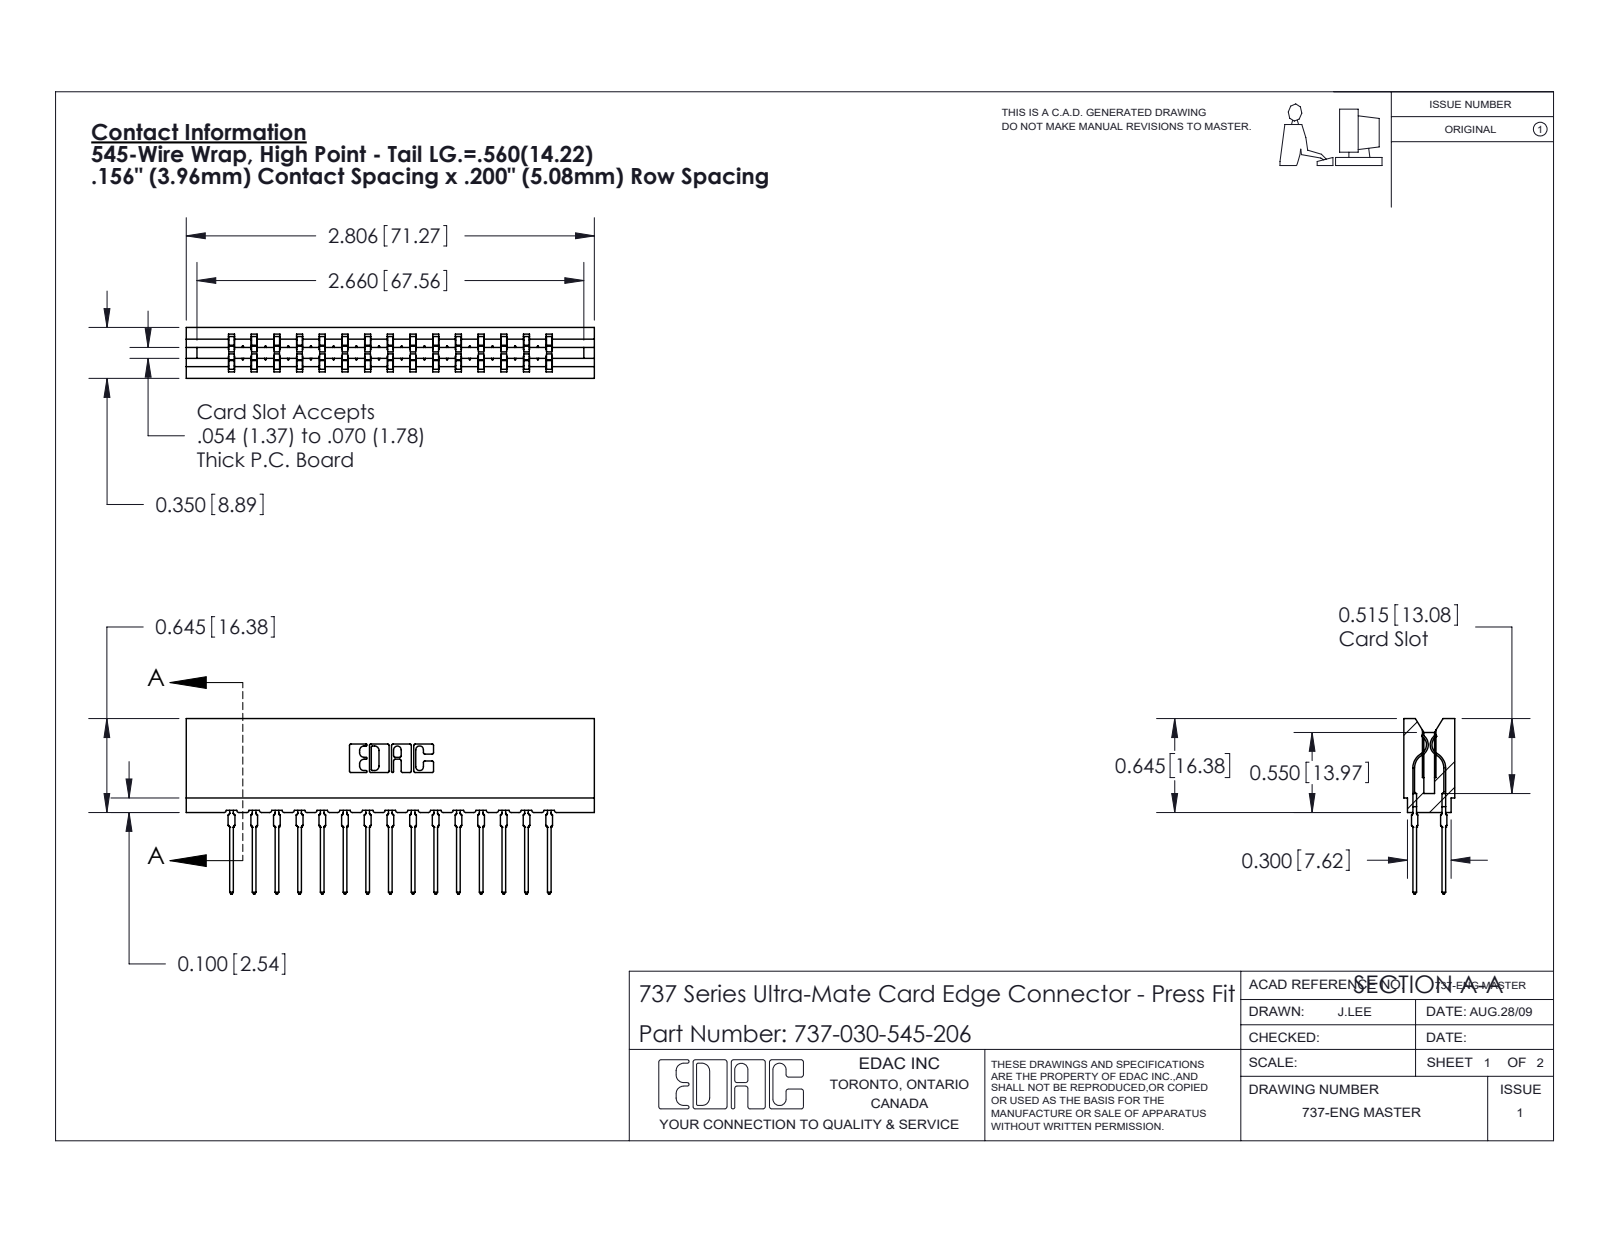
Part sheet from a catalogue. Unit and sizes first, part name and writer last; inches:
Units: inches
Overall size (bounding box): 2.806 × 1.206 × 0.35
Partial cylindrical surfaces — rounded edges, fillets, slot ends (radius × count): R0.021 ×60, R0.015 ×30, R0.01 ×22, R0.005 ×8, R0.011 ×8, R0.007 ×6, R0.031 ×6, R0.026 ×3
Main face-to-face distances: 0.138, 0.212, 0.35, 0.156, 0.624, 0.063, 0.287, 0.076, 0.149, 0.78
Volume: 0.446 in³ · Surface area: 16.33 in²
Bodies: 31 solids, 2795 faces (1450 planar, 565 cylindrical, 780 other)
Part name (STEP PRODUCT): 737 Part_Insulator Option - 06; 745-292-001_545; 737-030-545-206
STEP written by: SolidWorks 2020 (CONFIG_CONTROL_DESIGN)
